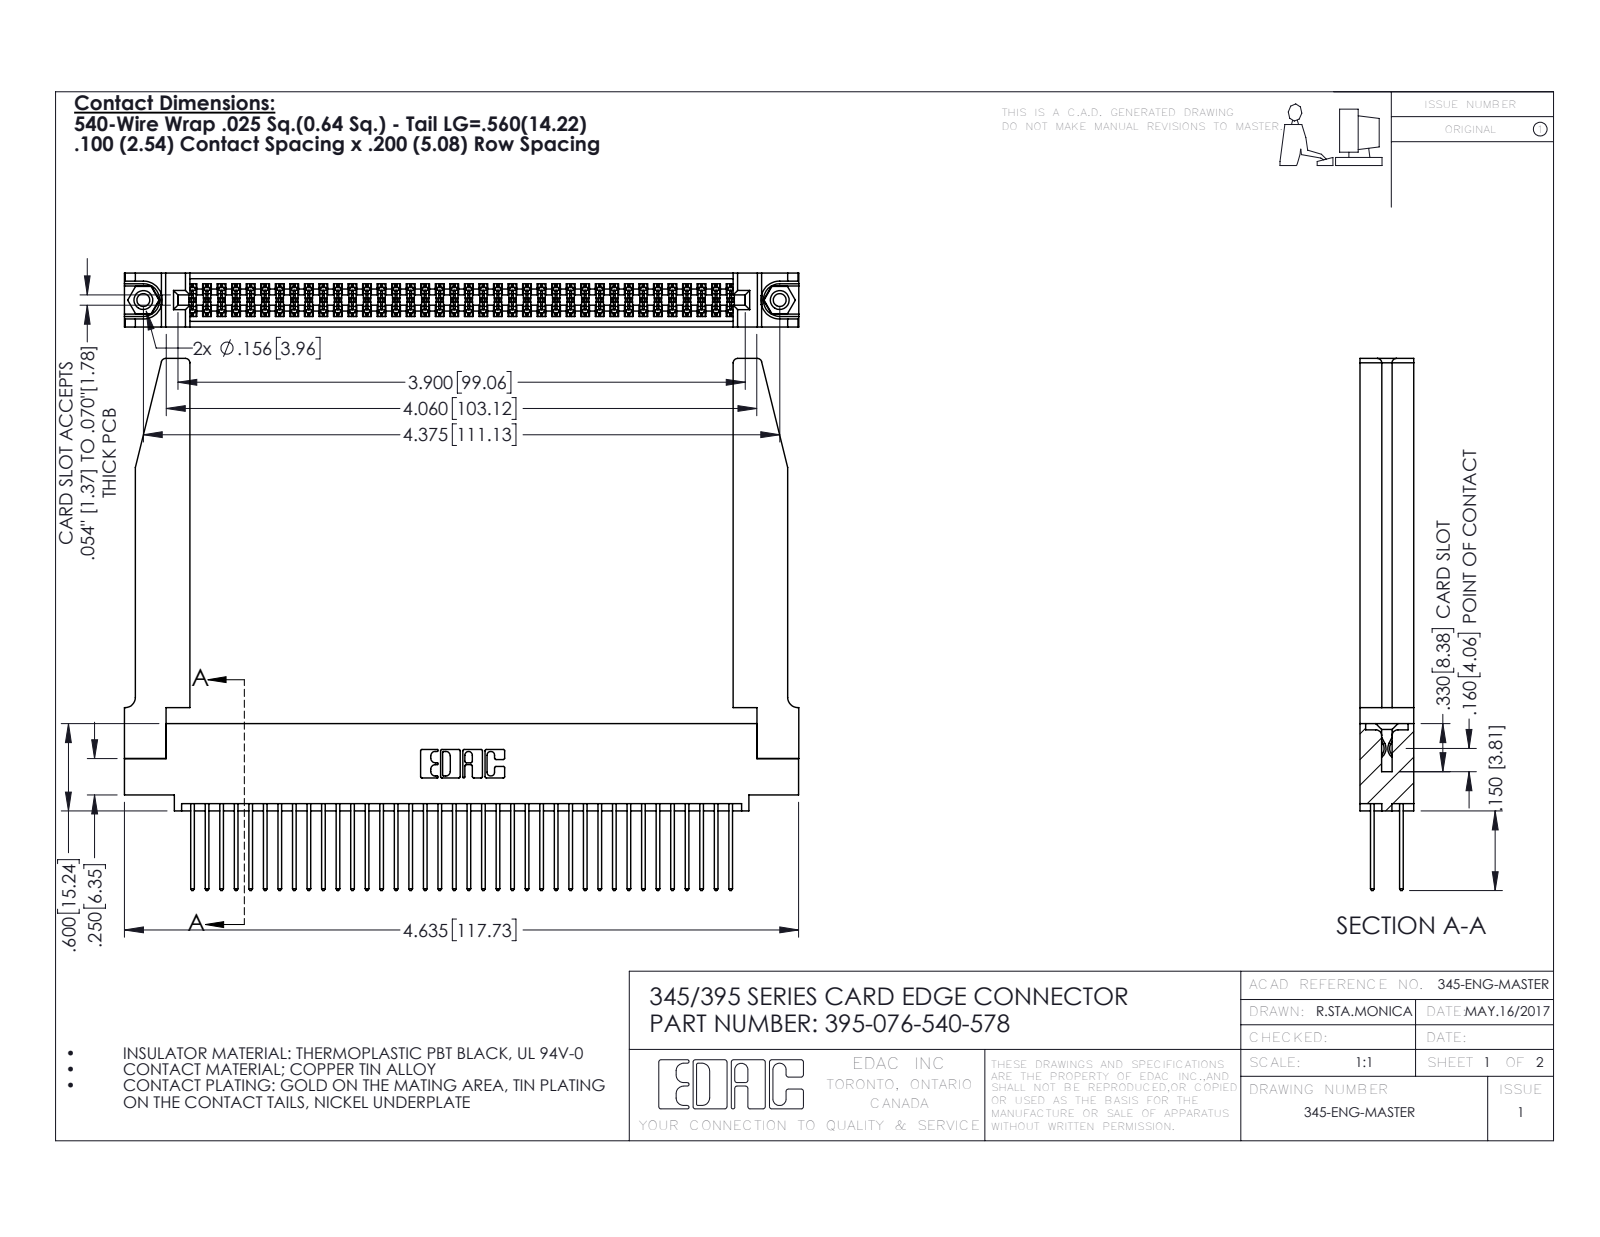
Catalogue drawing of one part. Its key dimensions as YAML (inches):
part_name: "345-220-078_345-220-078; 345 Part_0.110 Offset - 0.156 Dia-TH; 345-292-001_345-293-140; 395-076-540-578 (+1 more)"
step_written_by: "SolidWorks 2016 (CONFIG_CONTROL_DESIGN)"
units: inches
bodies: {solids: 81, faces: 4164, planar: 2734, cylindrical: 1378, other: 52}
overall_size: [4.636, 3.657, 0.37]
volume: 1.183
surface_area: 39.31
round_holes:
  - {diameter: 0.089, count: 2}
  - {diameter: 0.125, count: 2}
  - {diameter: 0.156, count: 2}
  - {diameter: 0.064, count: 1}
round_bosses_or_shafts:
  - {diameter: 0.155, count: 2}
partial_cylinders:
  - {radius: 0.006, count: 114}
  - {radius: 0.01, count: 76}
  - {radius: 0.01, count: 22}
  - {radius: 0.03, count: 8}
  - {radius: 0.007, count: 6}
  - {radius: 0.031, count: 6}
  - {radius: 0.026, count: 3}
  - {radius: 0.014, count: 2}
face_to_face_distances: [0.072, 0.298, 0.37, 0.2, 0.098, 0.272, 0.025, 0.225, 0.175, 0.148]
hole_center_spacings: [0.27, 4.139, 4.375]
